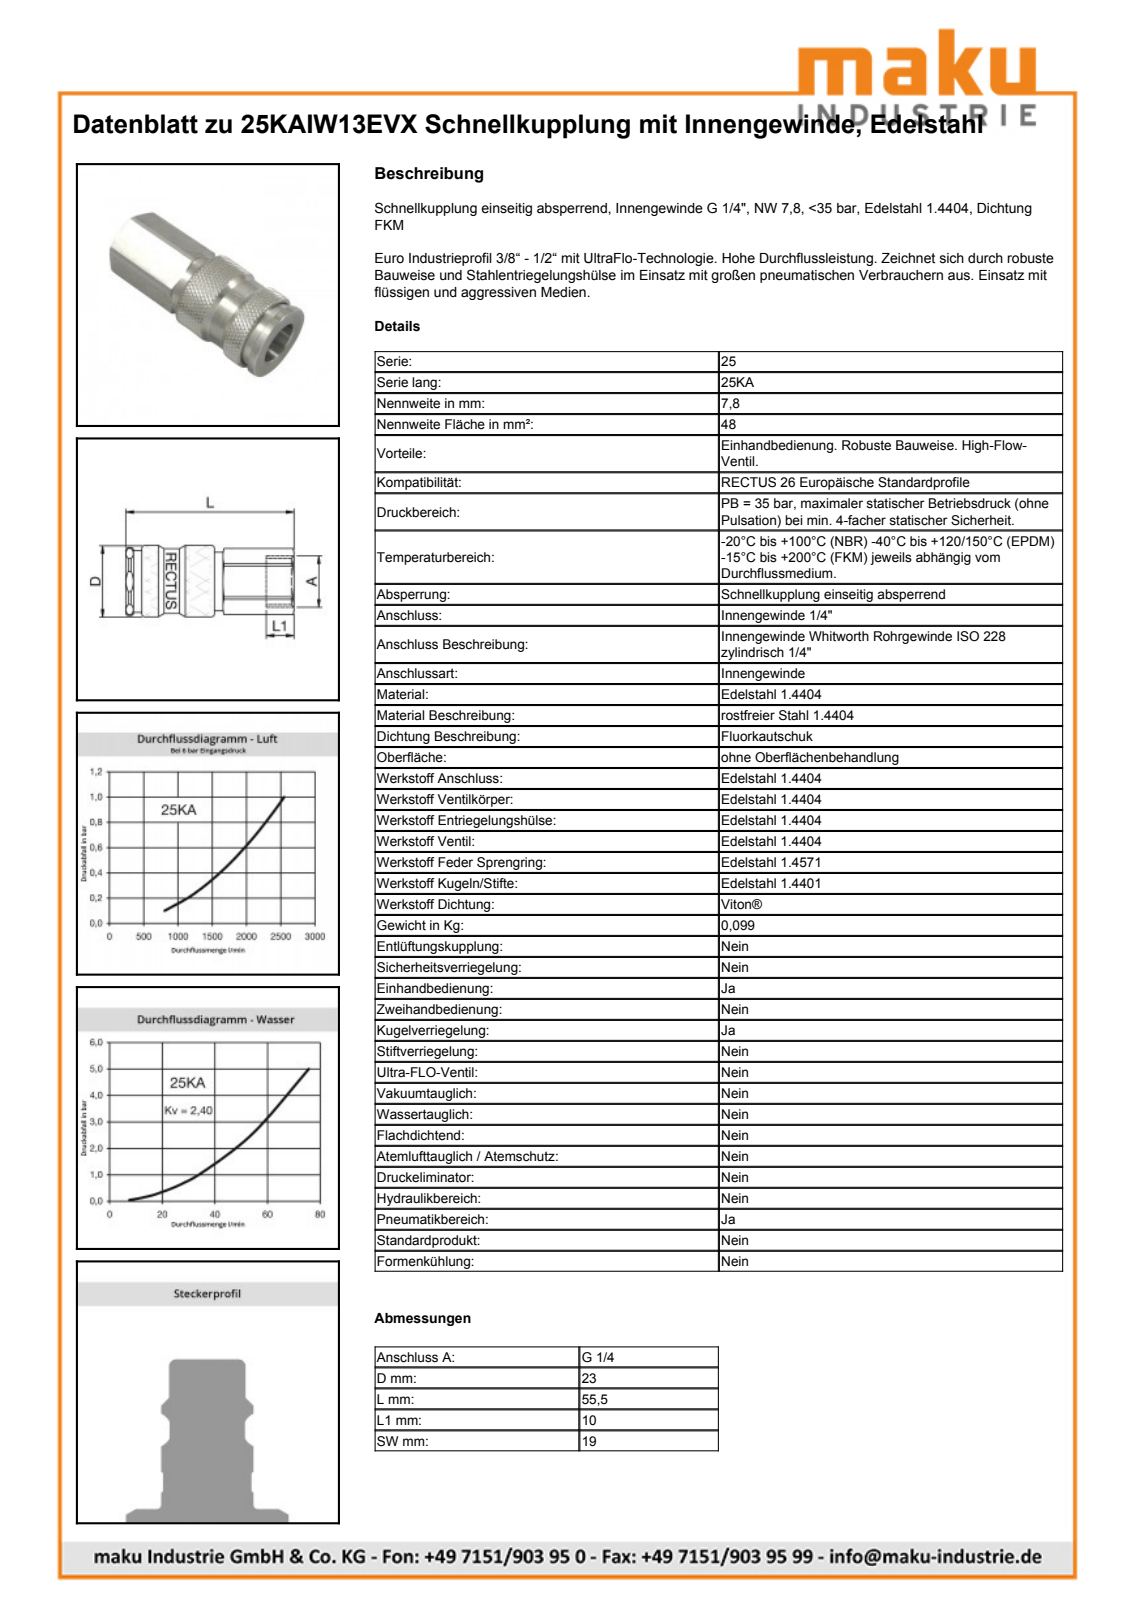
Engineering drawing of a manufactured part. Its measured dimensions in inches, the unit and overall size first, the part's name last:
Units: inches
Overall size (bounding box): 2.159 × 0.911 × 0.911
Round holes (diameter × count): ⌀0.45 ×1, ⌀0.594 ×1, ⌀0.63 ×1, ⌀0.679 ×1, ⌀0.762 ×1, ⌀0.789 ×1
Round bosses / shafts (diameter × count): ⌀0.911 ×1, ⌀0.827 ×1, ⌀0.787 ×1, ⌀0.746 ×1, ⌀0.602 ×1, ⌀0.591 ×1, ⌀0.579 ×1
Partial cylindrical surfaces — rounded edges, fillets, slot ends (radius × count): R0.409 ×1, R0.421 ×1, R0.433 ×1
Main face-to-face distances: 0.748, 2.159, 0.827, 1.766, 0.394, 0.939, 1.22, 0.636, 1.13, 0.191
Volume: 1.029 in³ · Surface area: 12.82 in²
Bodies: 2 solids, 562 faces (215 planar, 73 cylindrical, 274 other)
Part name (STEP PRODUCT): D107409
STEP written by: Autodesk Inventor 2013 (AUTOMOTIVE_DESIGN)
